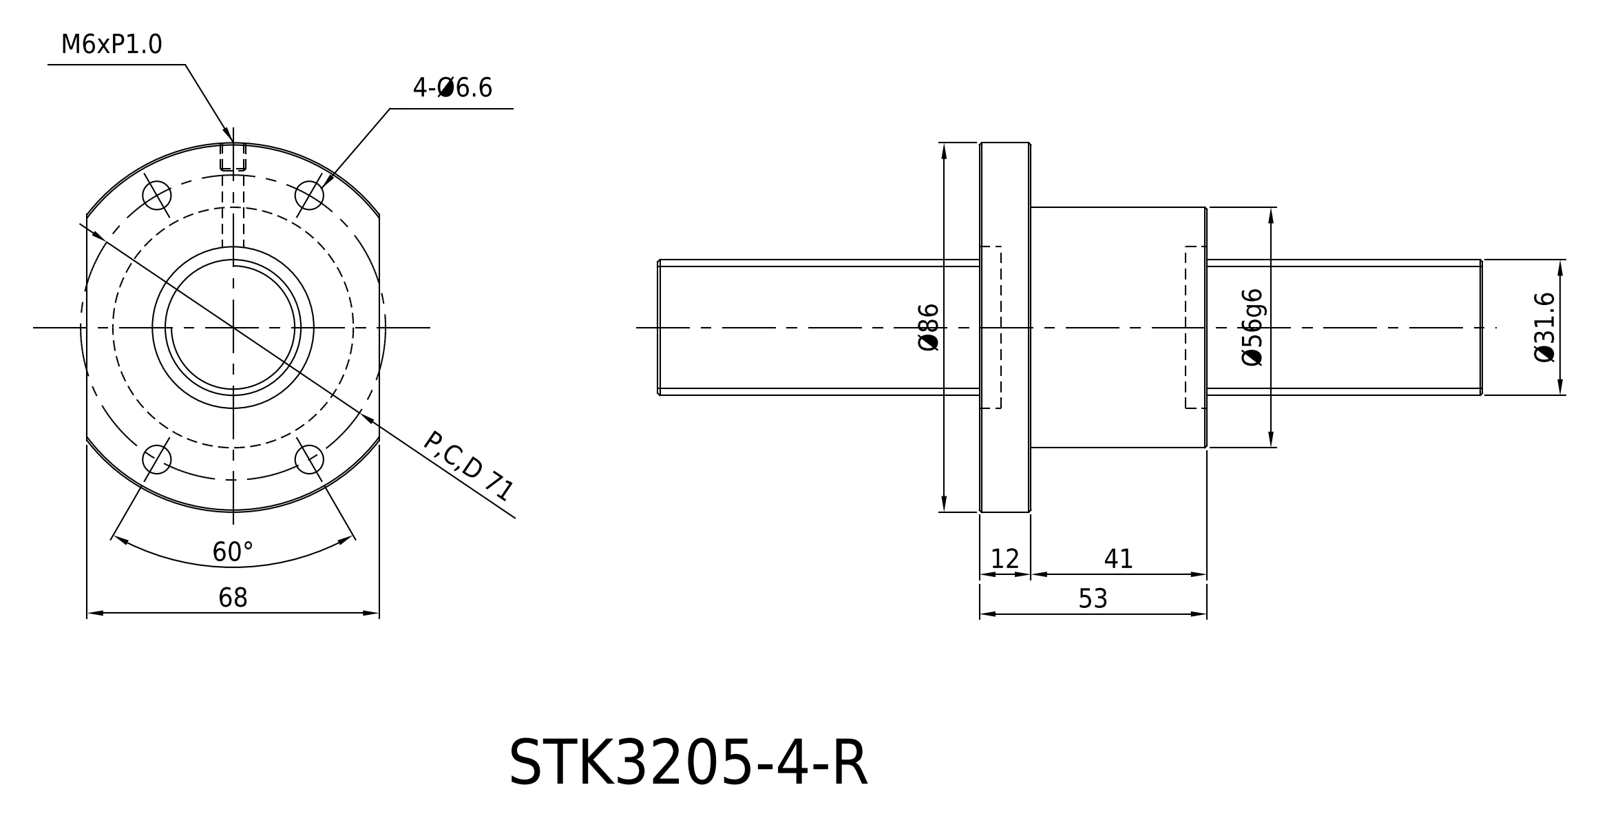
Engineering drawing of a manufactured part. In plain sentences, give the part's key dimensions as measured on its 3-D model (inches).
The part is named "3205 STK". Its 3-D file was written by "CATIA V5 STEP AP214 (AUTOMOTIVE_DESIGN)". It is 1 solid with 45 faces: 5 planar, 14 cylindrical and 26 other. Overall it measures 3.386 by 2.677 by 2.087 inches. Its volume is 7.235 cubic inches and its surface area 38.56 square inches. Round holes: 4 of diameter 0.26, 1 of diameter 1.26. Round bosses or shafts: 1 of diameter 2.205. Partial cylindrical surfaces (rounded edges, fillets, slot ends): 1 of radius 1.693. The main face-to-face distances are 0.472, 1.614, 2.087, 2.677. The hole center spacings are 1.339, 2.318, 2.677.
